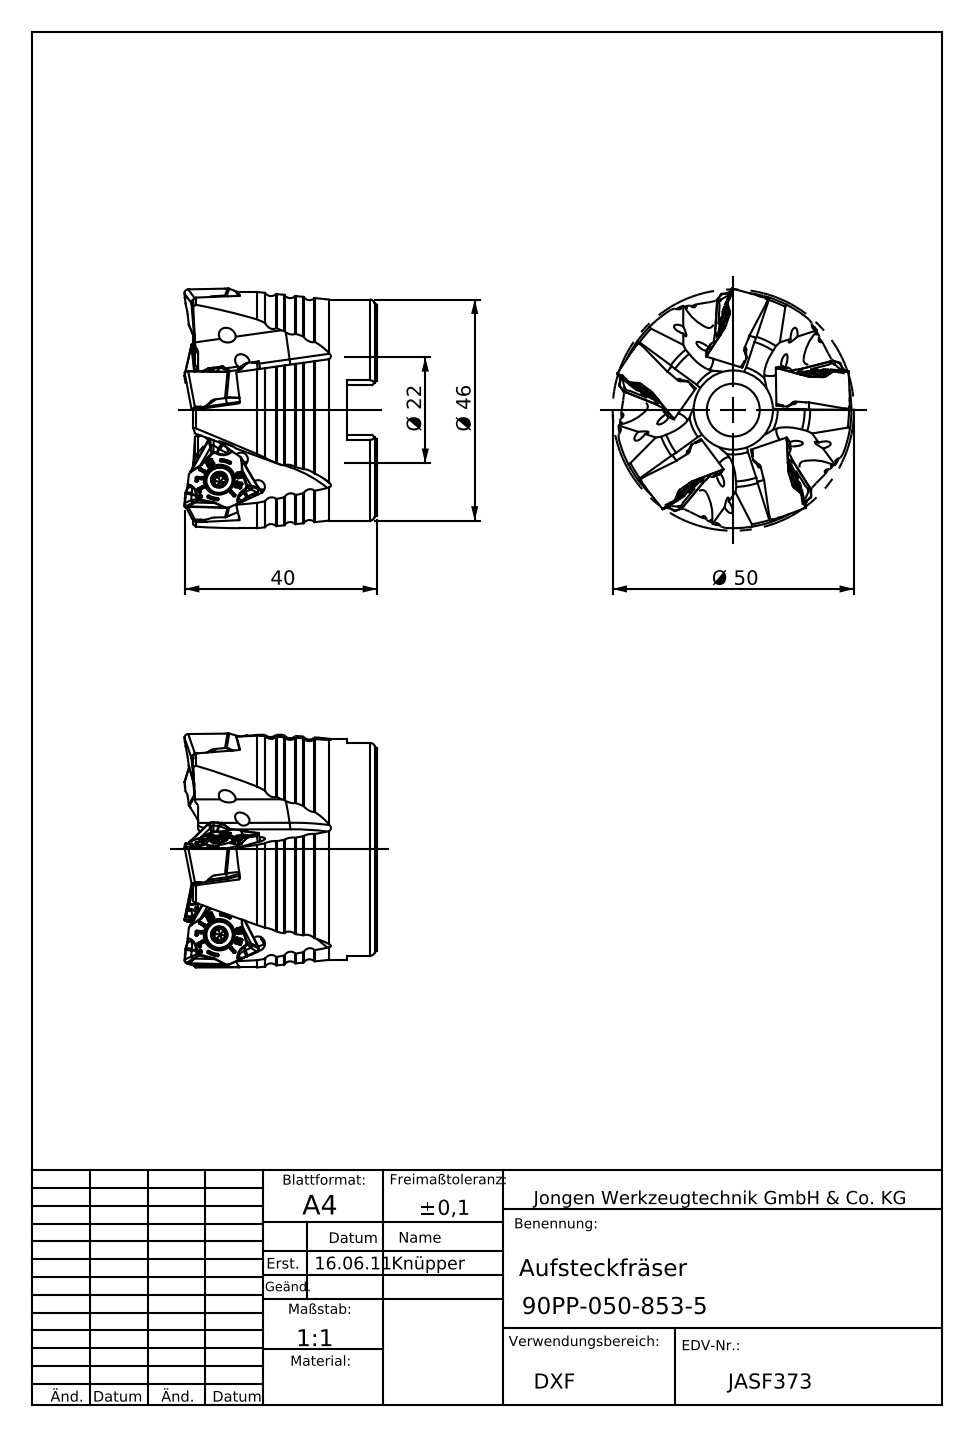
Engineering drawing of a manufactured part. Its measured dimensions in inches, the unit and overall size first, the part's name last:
Units: inches
Overall size (bounding box): 1.969 × 1.969 × 1.575
Round holes (diameter × count): ⌀0.118 ×5, ⌀0.433 ×1, ⌀0.65 ×1, ⌀0.866 ×1, ⌀0.872 ×1, ⌀0.878 ×1
Round bosses / shafts (diameter × count): ⌀1.969 ×1, ⌀1.935 ×1, ⌀1.811 ×1
Partial cylindrical surfaces — rounded edges, fillets, slot ends (radius × count): R0.012 ×35, R0.059 ×10
Main face-to-face distances: 0.256, 0.25, 0.907, 0.657, 0.059, 1.506, 1.256, 0.598, 1.073, 0.823
Volume: 3.052 in³ · Surface area: 23.44 in²
Bodies: 1 solid, 364 faces (93 planar, 92 cylindrical, 179 other)
Part name (STEP PRODUCT): 90PP-050-853-5
STEP written by: SolidWorks 2010 (AUTOMOTIVE_DESIGN)
